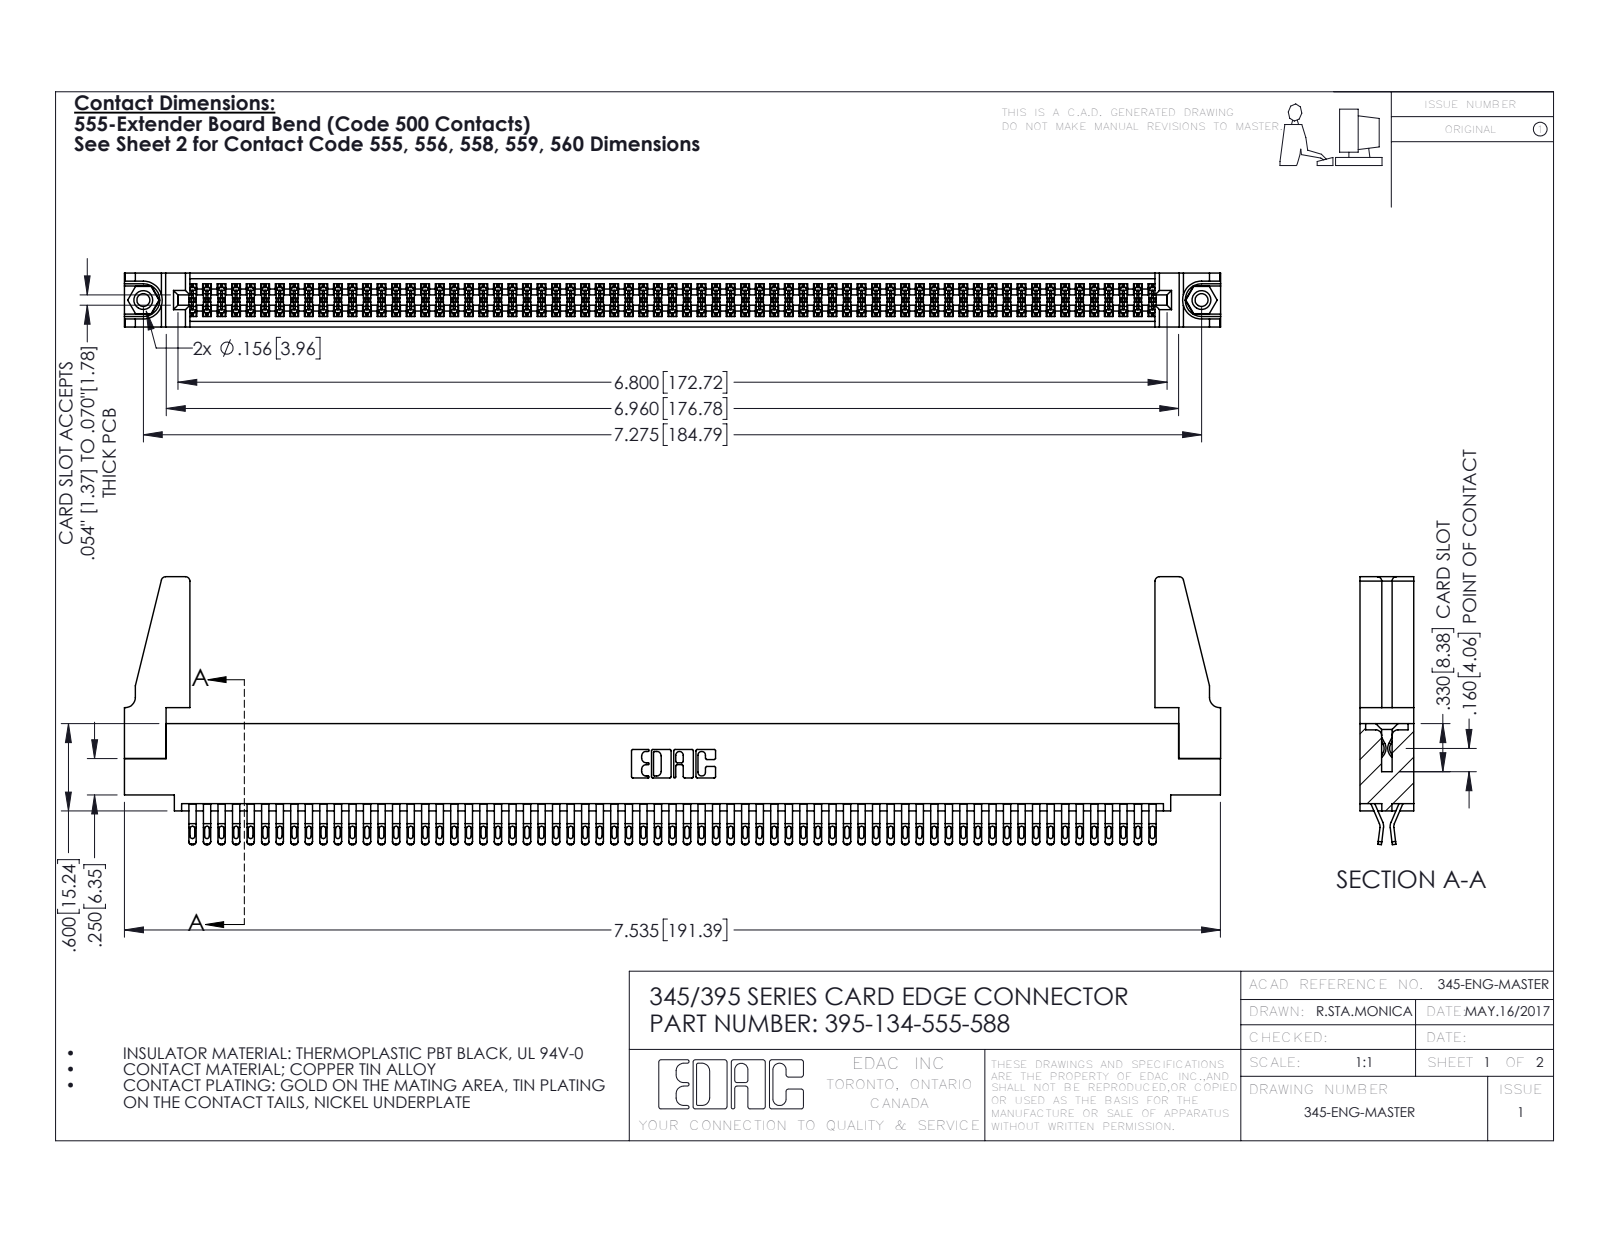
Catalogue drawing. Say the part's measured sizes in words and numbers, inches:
The part is named "345-220-078_345-220-088; 345-292-001_555 Tail; 345-250-001_345-250-001-102; 345 Part_0.110 Offset - 0.156 Dia-TH (+1 more)". Its 3-D file was written by "SolidWorks 2016 (CONFIG_CONTROL_DESIGN)". It is 139 solids with 7758 faces: 4310 planar, 3432 cylindrical and 16 other. Overall it measures 7.536 by 1.842 by 0.37 inches. Its volume is 1.367 cubic inches and its surface area 51.69 square inches. Round holes: 2 of diameter 0.089, 2 of diameter 0.125, 2 of diameter 0.156, 1 of diameter 0.064. Round bosses or shafts: 2 of diameter 0.155. Partial cylindrical surfaces (rounded edges, fillets, slot ends): 335 of radius 0.016, 268 of radius 0.02, 201 of radius 0.006, 22 of radius 0.01, 8 of radius 0.03, 6 of radius 0.007, 6 of radius 0.031, 3 of radius 0.026. The main face-to-face distances are 0.072, 0.298, 0.37, 0.025, 0.098, 0.272, 0.2, 0.225, 0.175, 0.149. The hole center spacings are 0.27, 7.039, 7.275.
